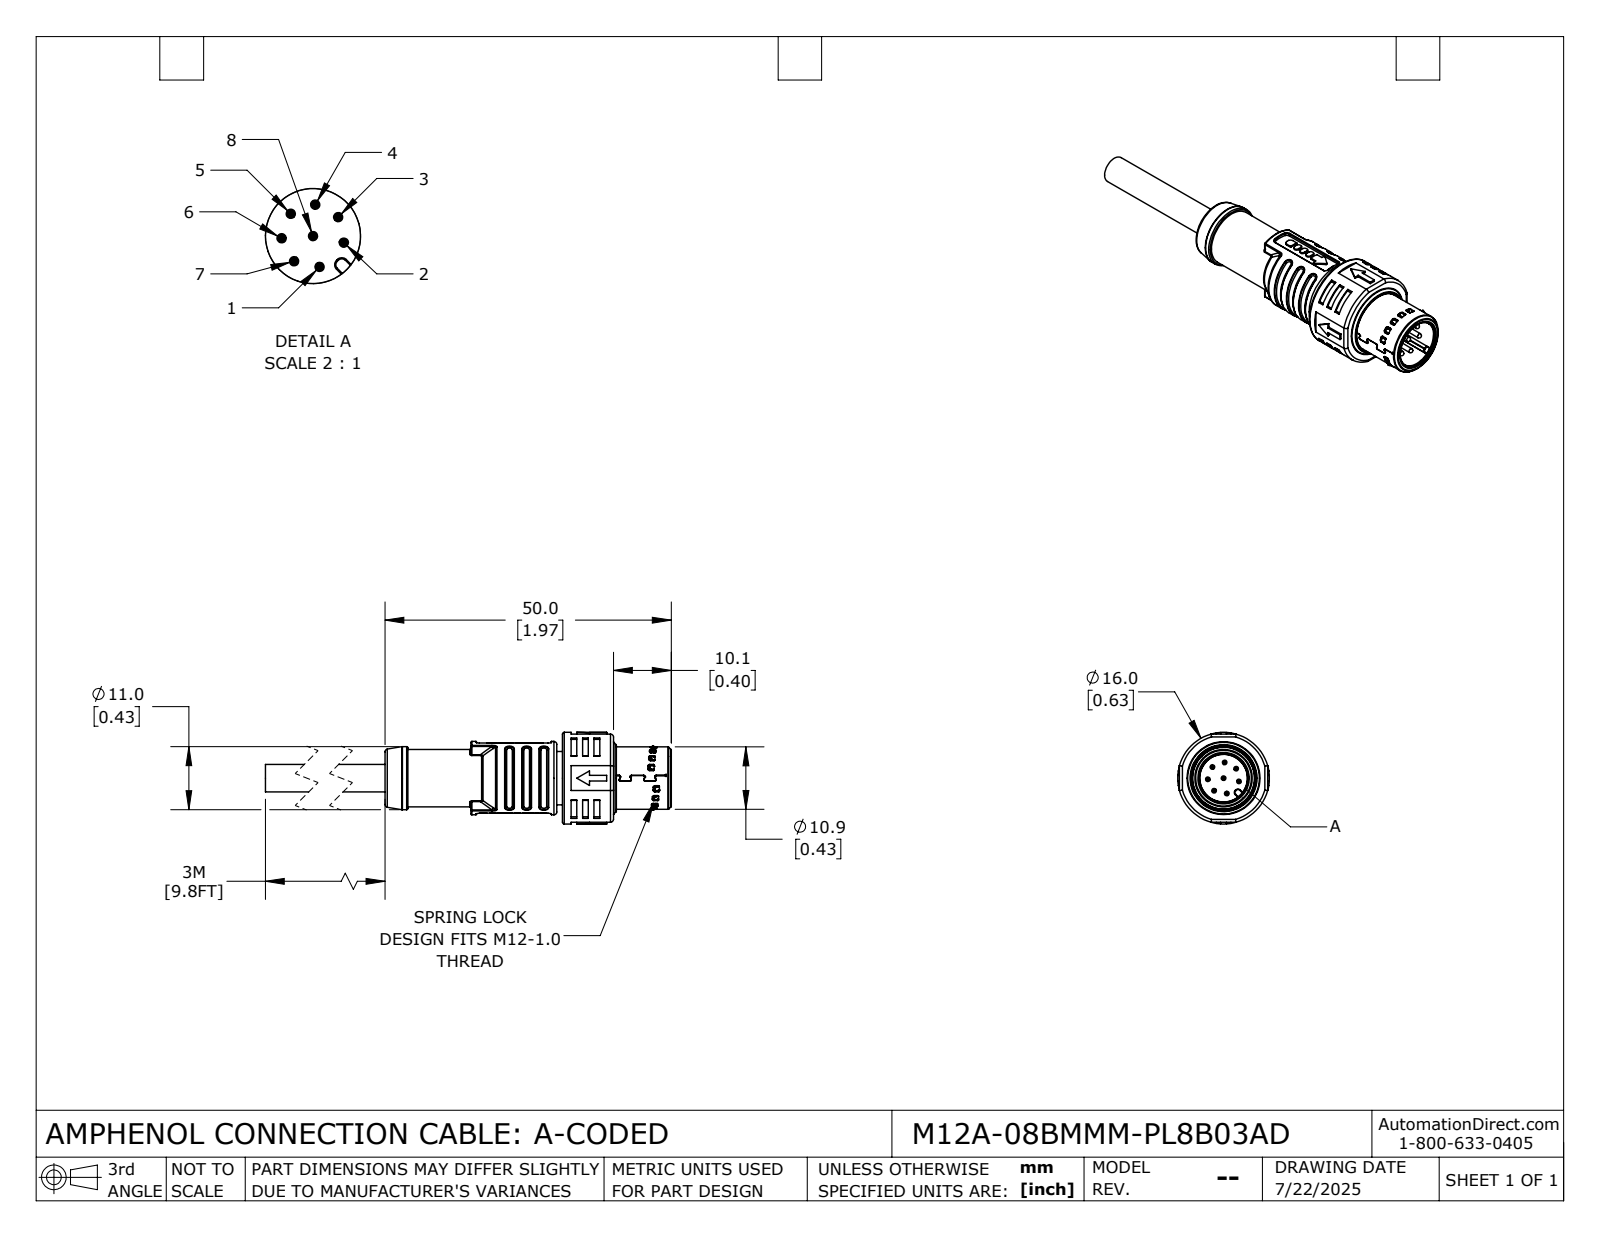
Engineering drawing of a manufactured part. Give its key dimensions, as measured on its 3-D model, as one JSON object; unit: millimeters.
{"part_name": "M12A-08BMMM-PL8B03AD", "step_written_by": "SolidWorks 2024 (CONFIG_CONTROL_DESIGN)", "units": "millimeters", "bodies": {"solids": 1, "faces": 2027, "planar": 880, "cylindrical": 644, "other": 503}, "overall_size": [75, 16, 16], "volume_mm3": 5223, "surface_area_mm2": 5723, "round_holes": [[8.3, 1], [9, 1], [10.15, 1], [10.5, 1], [10.9, 1], [11.5, 1], [11.8, 1], [14.2, 1]], "round_bosses_or_shafts": [[0.8, 8], [16, 1], [14.1, 1], [12.8, 1], [12.4, 1], [11, 1], [10.45, 1], [10.4, 1]], "partial_cylinders_radius": [[0.2, 114], [0.25, 66], [0.3, 64], [0.15, 44], [0.5, 38], [0.13, 12], [0.7, 11], [0.1, 10]], "face_to_face_distances": [1, 10.1, 8.6, 8.9, 2.5, 1.5, 1.2, 32.5, 15.4, 41.1]}
